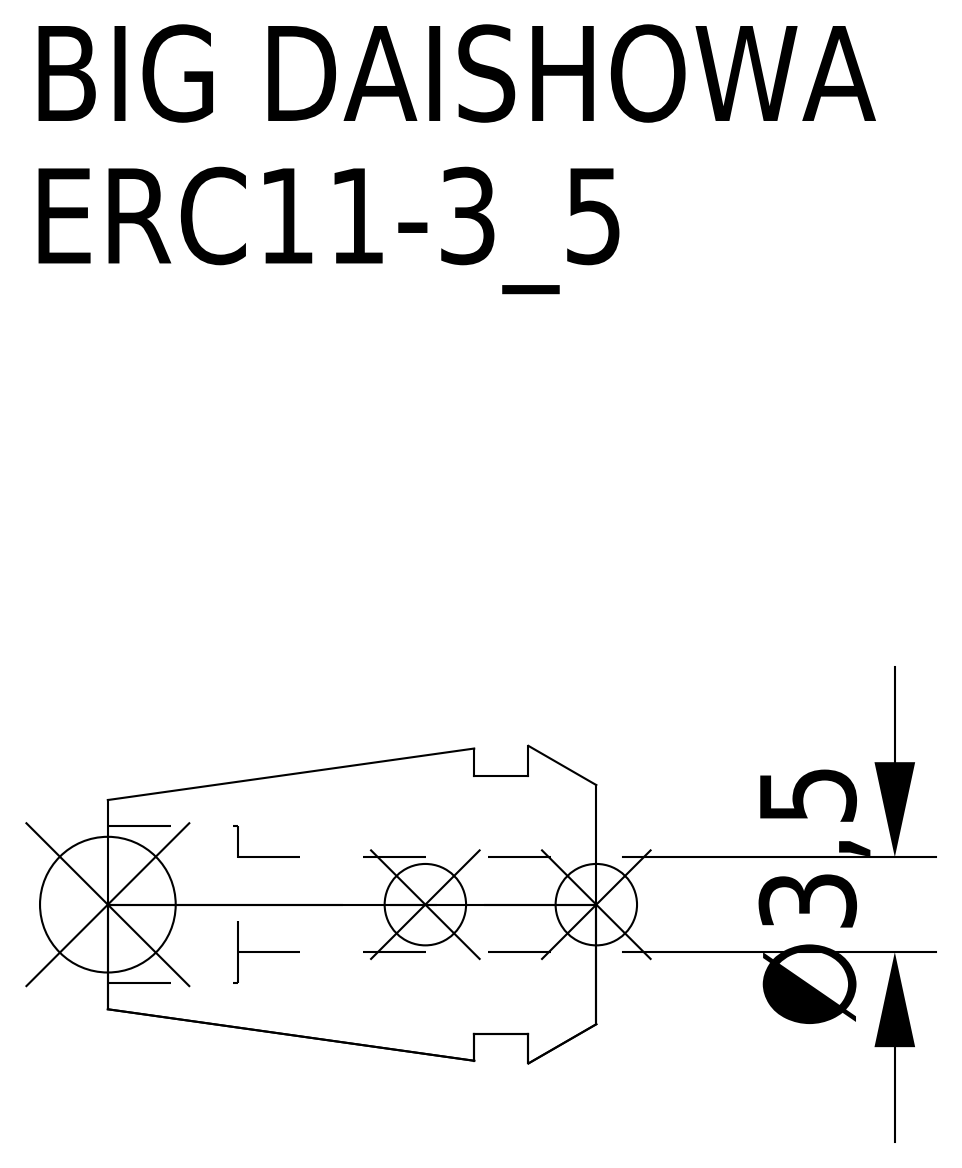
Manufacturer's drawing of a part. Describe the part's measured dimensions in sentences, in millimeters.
The part is named "ERC11-3_5". Its 3-D file was written by "CREO PARAMETRIC BY PTC INC, 2016380 (AUTOMOTIVE_DESIGN)". It is 1 solid with 15 faces: 5 planar, 6 cylindrical and 4 other. Overall it measures 18 by 11.7 by 11.7 millimeters. Its volume is 1 088 cubic millimeters and its surface area 955 square millimeters. Round holes: 1 of diameter 3.5, 1 of diameter 5.8. Round bosses or shafts: 1 of diameter 9.5. The main face-to-face distances are 2.5, 4.5, 2, 18, 15.5, 13.5, 13.22, 10.72, 8.72, 4.78.
